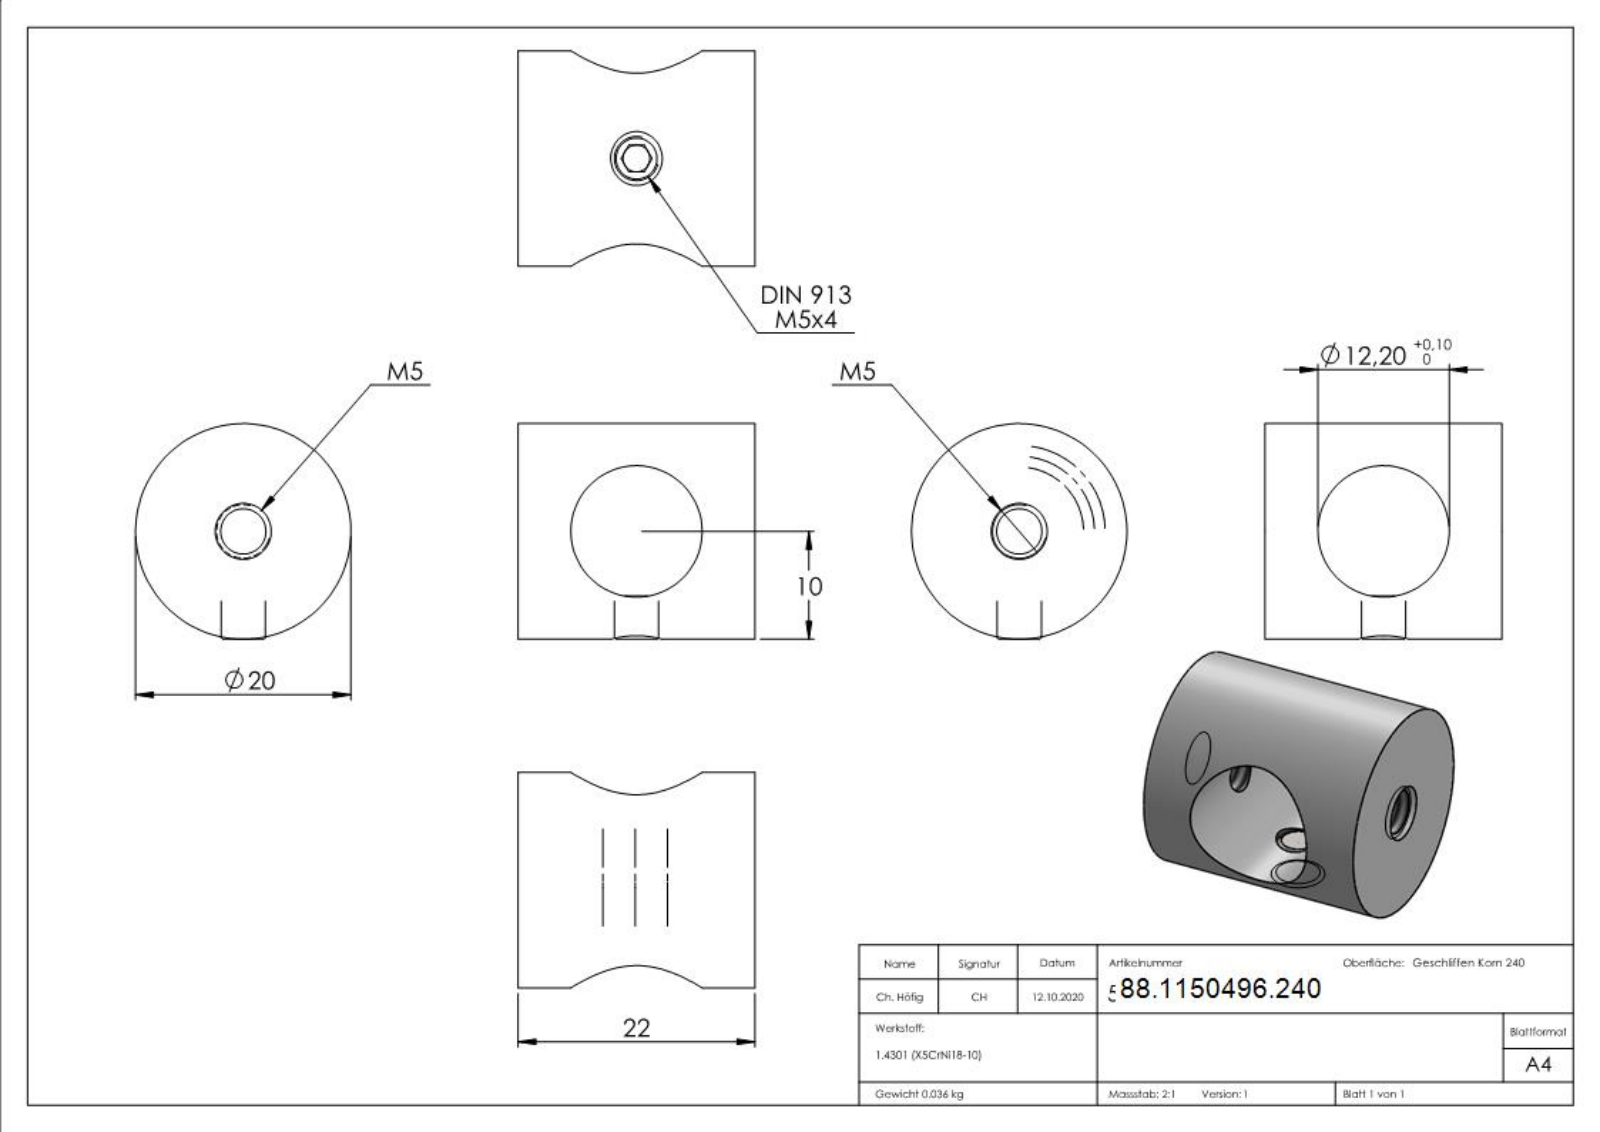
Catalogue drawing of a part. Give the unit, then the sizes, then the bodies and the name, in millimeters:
Units: millimetres
Overall size (bounding box): 70 × 22 × 20
Round holes (diameter × count): ⌀4.2 ×2, ⌀12.2 ×1
Round bosses / shafts (diameter × count): ⌀20 ×1, ⌀5 ×1
Main face-to-face distances: 22, 2.5, 4, 3, 1
Volume: 4 543 mm³ · Surface area: 2 659 mm²
Bodies: 2 solids, 40 faces (16 planar, 12 cylindrical, 12 other)
Part name (STEP PRODUCT): 50496-240; 5049X-240 Teil1_50496-240 Teil1; DIN913_DIN 913 M5x4; DIN913 (+1 more)
STEP written by: SolidWorks 2018 (CONFIG_CONTROL_DESIGN)
